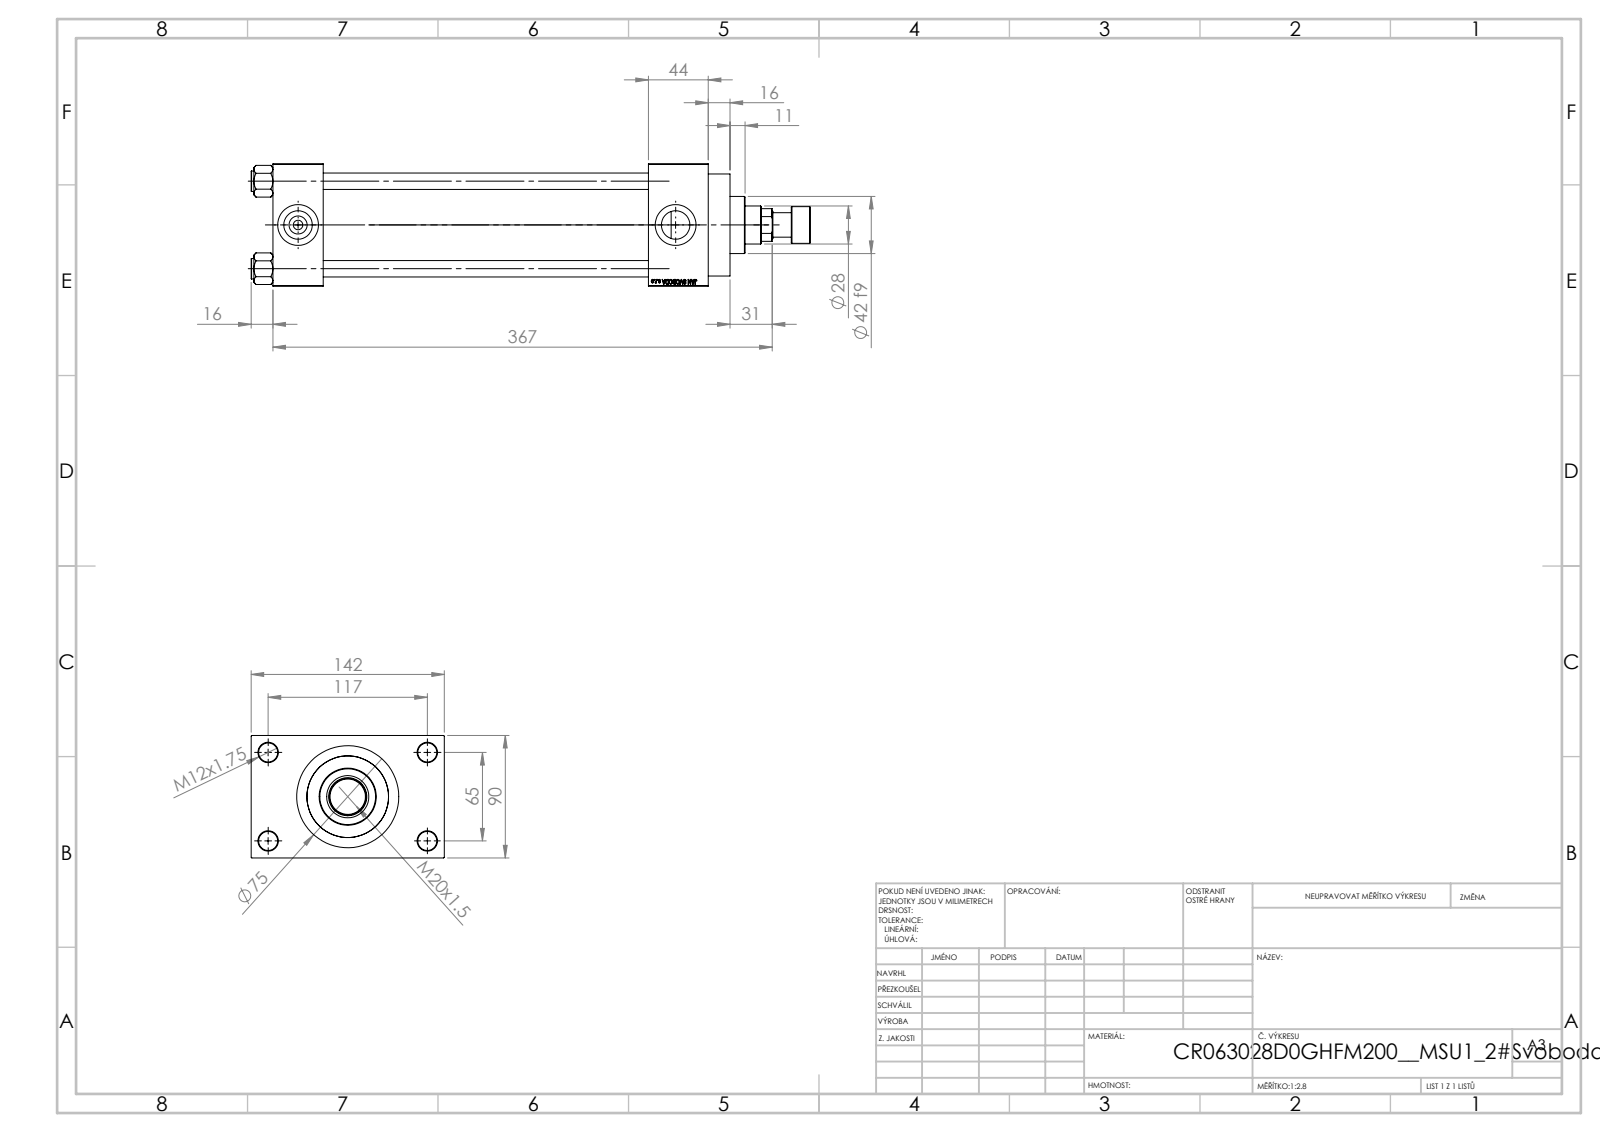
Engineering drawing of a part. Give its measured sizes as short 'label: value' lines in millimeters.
name: V215CR_VCP_D; V215_VC_A; V215CR_D_Body; NUT_M5_D (+2 more)
written by: SolidWorks 2019 (CONFIG_CONTROL_DESIGN)
unit: mm
bodies: 12 solids, 1117 faces (501 planar, 92 cylindrical, 524 other)
size: 411 × 142 × 90
volume: 1 412 000 mm³; area: 321 191 mm²
holes: 4× ⌀12, 4× ⌀14, 2× ⌀7, 2× ⌀20.96, 2× ⌀30, 1× ⌀18.5, 1× ⌀28, 1× ⌀31, 1× ⌀50, 1× ⌀60, 1× ⌀63
bosses: 4× ⌀15, 1× ⌀75, 1× ⌀69, 1× ⌀42, 1× ⌀27, 1× ⌀18
face distances: 90, 239, 37, 276, 283, 320, 44, 26, 116, 16
hole spacings: 26.35, 45.47, 64.3, 66.92, 69.81, 90.65, 111.34, 65
